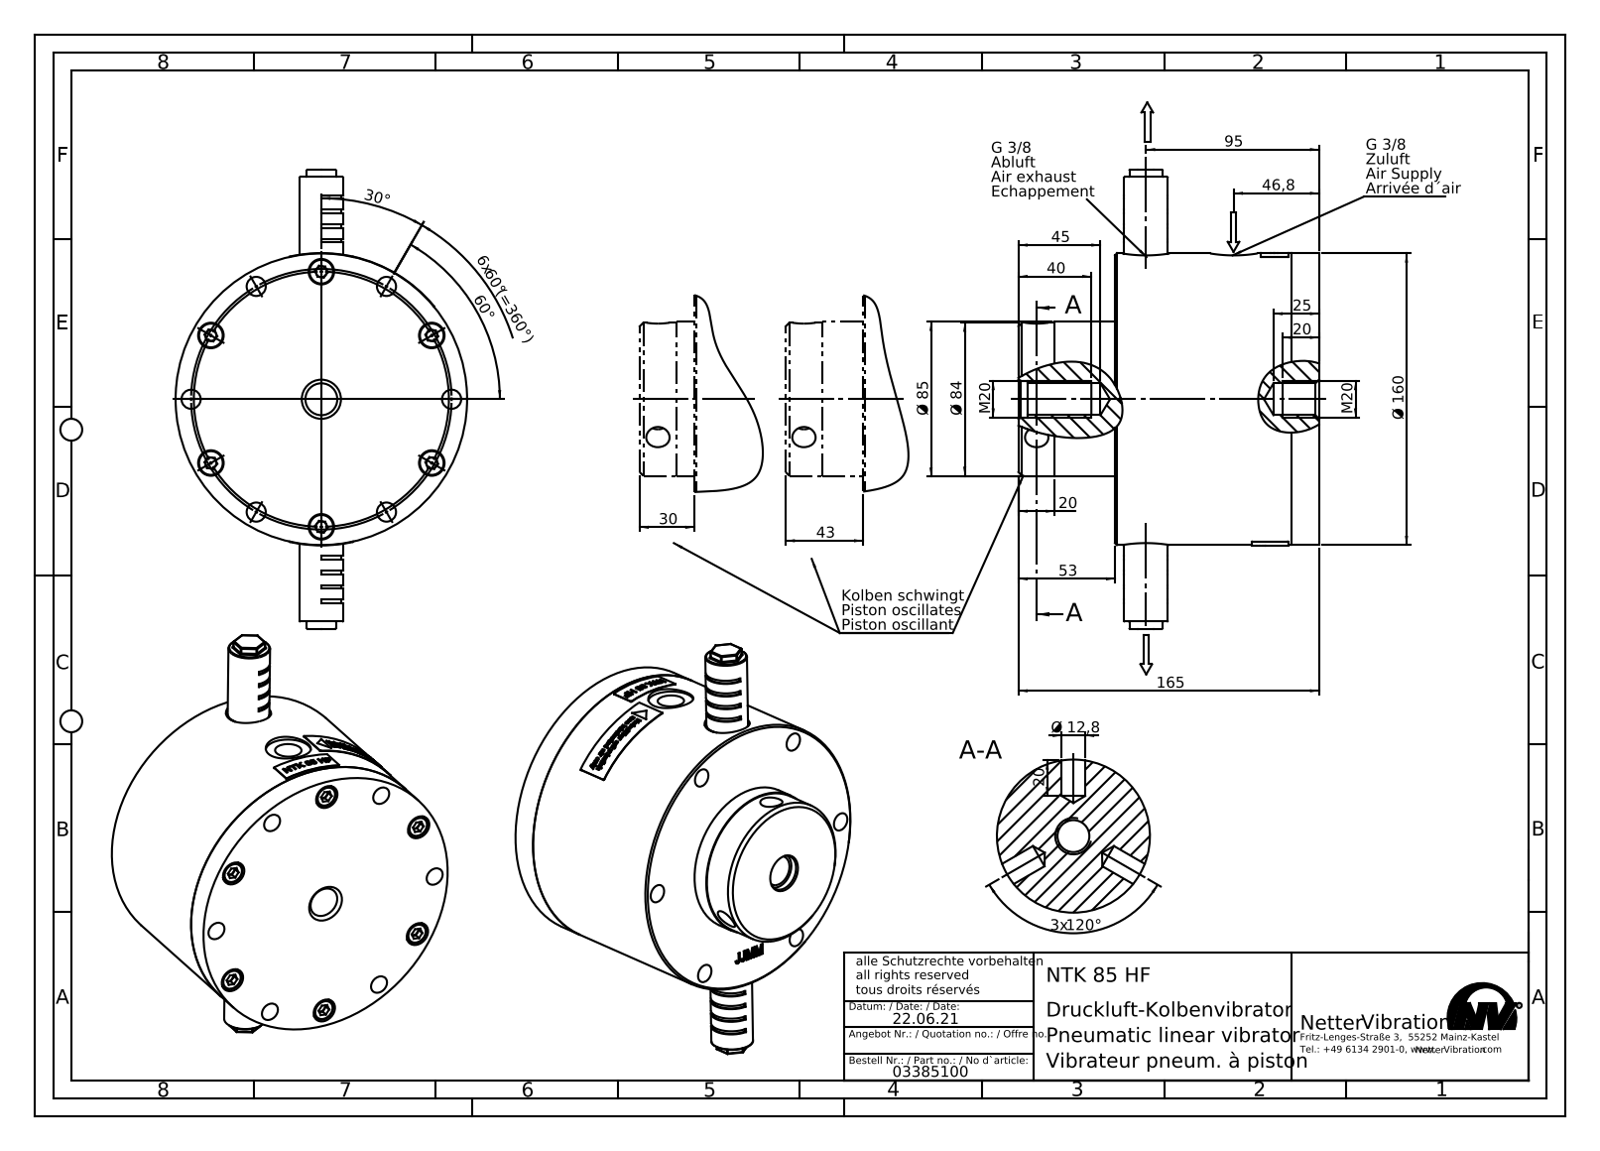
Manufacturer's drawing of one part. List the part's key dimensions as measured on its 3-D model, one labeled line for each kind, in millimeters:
Part name (STEP PRODUCT): NTK 85 HF #03385100
STEP written by: SolidWorks 2015 (AUTOMOTIVE_DESIGN)
Units: millimetres
Bodies: 13 solids, 575 faces (167 planar, 270 cylindrical, 138 other)
Overall size (bounding box): 252 × 160 × 142
Volume: 2 385 000 mm³ · Surface area: 236 015 mm²
Round holes (diameter × count): ⌀8.5 ×6, ⌀10.5 ×6, ⌀14 ×6, ⌀12.8 ×3, ⌀14.95 ×2, ⌀26 ×2, ⌀17.5 ×1, ⌀85 ×1
Round bosses / shafts (diameter × count): ⌀13 ×6, ⌀8 ×6, ⌀160 ×1, ⌀84 ×1, ⌀24 ×1, ⌀22 ×1, ⌀16.66 ×1
Partial cylindrical surfaces — rounded edges, fillets, slot ends (radius × count): R0.5 ×38, R80.2 ×1
Main face-to-face distances: 15, 97, 112, 52, 55, 45, 3, 42, 57, 60
Hole centre spacings: 36.65, 70, 71.5, 100.06, 136.68, 121.24, 123.84, 140
